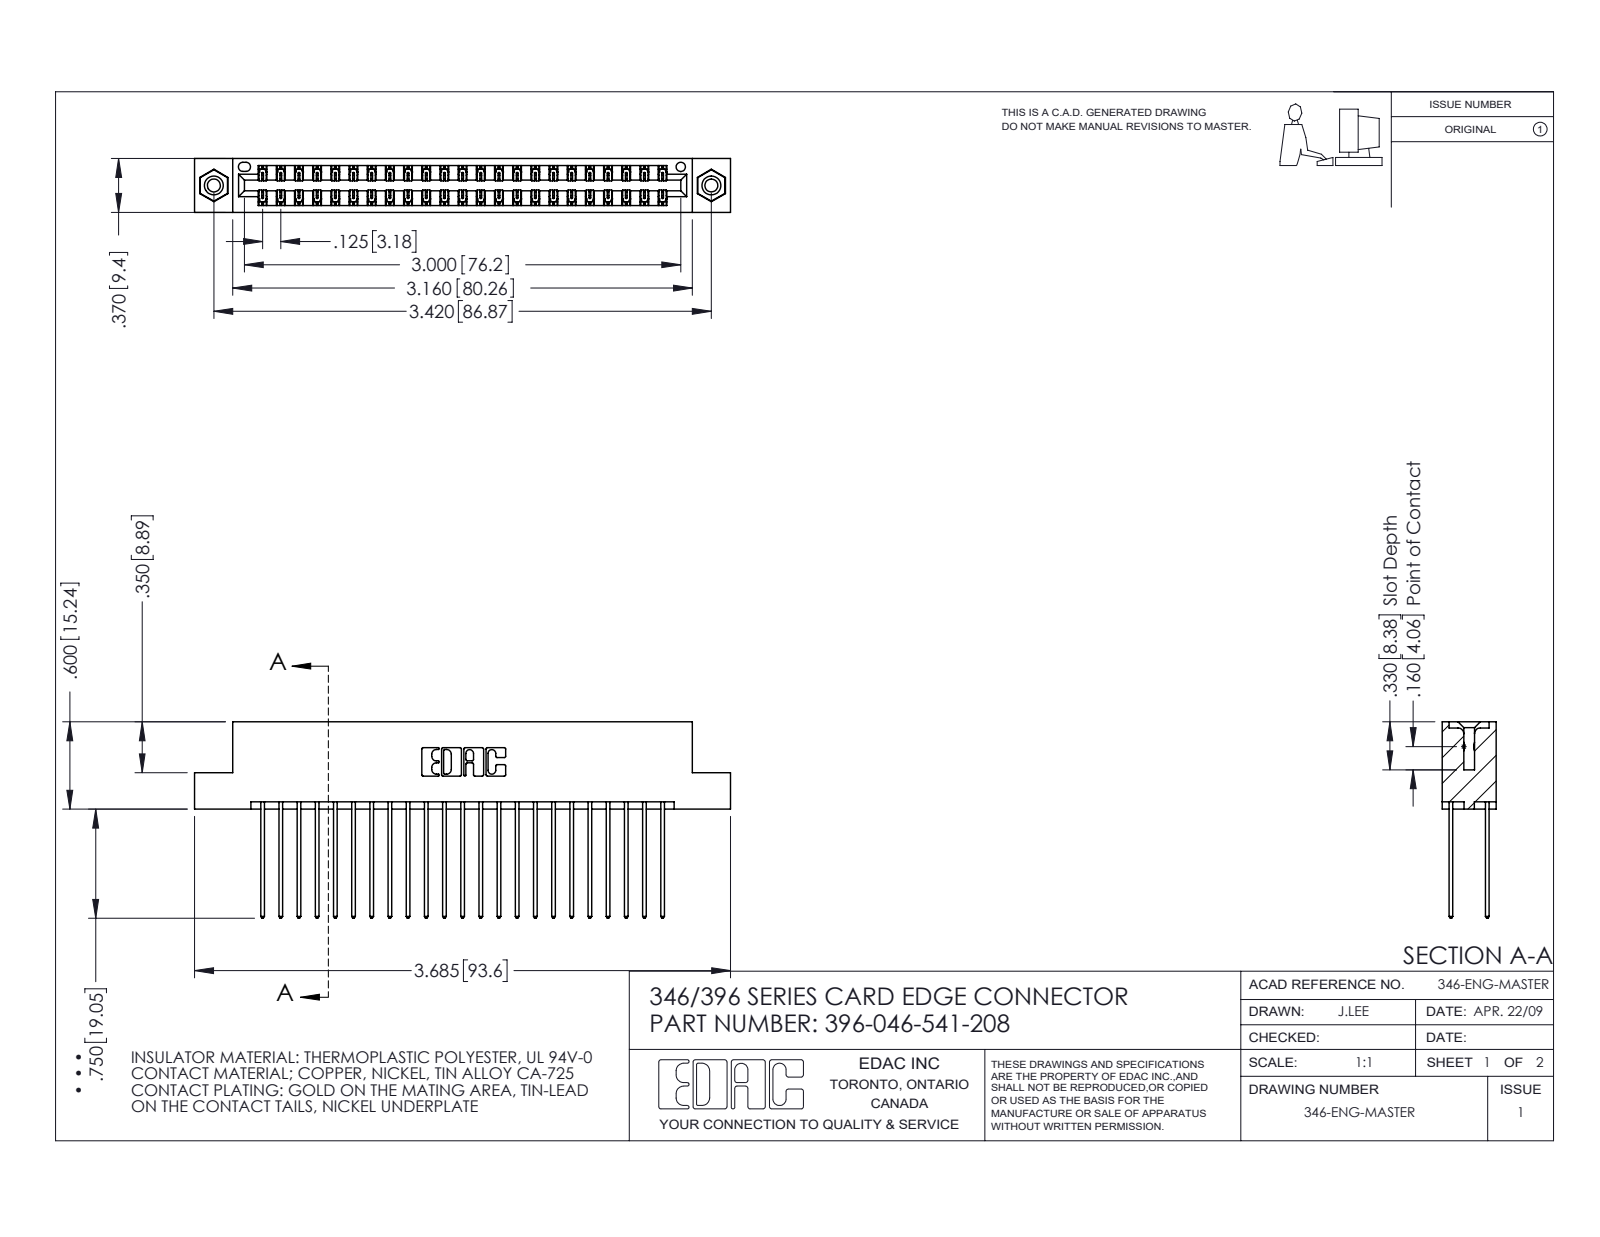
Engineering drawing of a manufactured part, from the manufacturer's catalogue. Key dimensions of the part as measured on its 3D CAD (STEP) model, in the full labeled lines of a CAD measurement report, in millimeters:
Part name (STEP PRODUCT): 396-046-541-208; 345-292-001_345-293-141; 346 Part_Flush Mounting Lugs - 0.156 Dia-TI; 345-250-001_345-250-003-102
STEP written by: SolidWorks 2016 (CONFIG_CONTROL_DESIGN)
Units: millimetres
Bodies: 49 solids, 2574 faces (1718 planar, 840 cylindrical, 16 other)
Overall size (bounding box): 93.6 × 34.3 × 9.4
Volume: 9 240 mm³ · Surface area: 13 680 mm²
Round holes (diameter × count): ⌀2.3 ×2, ⌀3.2 ×2, ⌀4 ×2, ⌀1.6 ×1
Round bosses / shafts (diameter × count): ⌀3.9 ×2
Partial cylindrical surfaces — rounded edges, fillets, slot ends (radius × count): R0.2 ×69, R0.3 ×46, R0.3 ×22, R0.2 ×6, R0.8 ×6, R0.7 ×3, R0.4 ×2, R0.6 ×2
Main face-to-face distances: 1.2, 8.2, 6.4, 1.8, 7.6, 0.6, 9.4, 7, 3.8, 5.6
Hole centre spacings: 6.2, 81.6, 86.9
